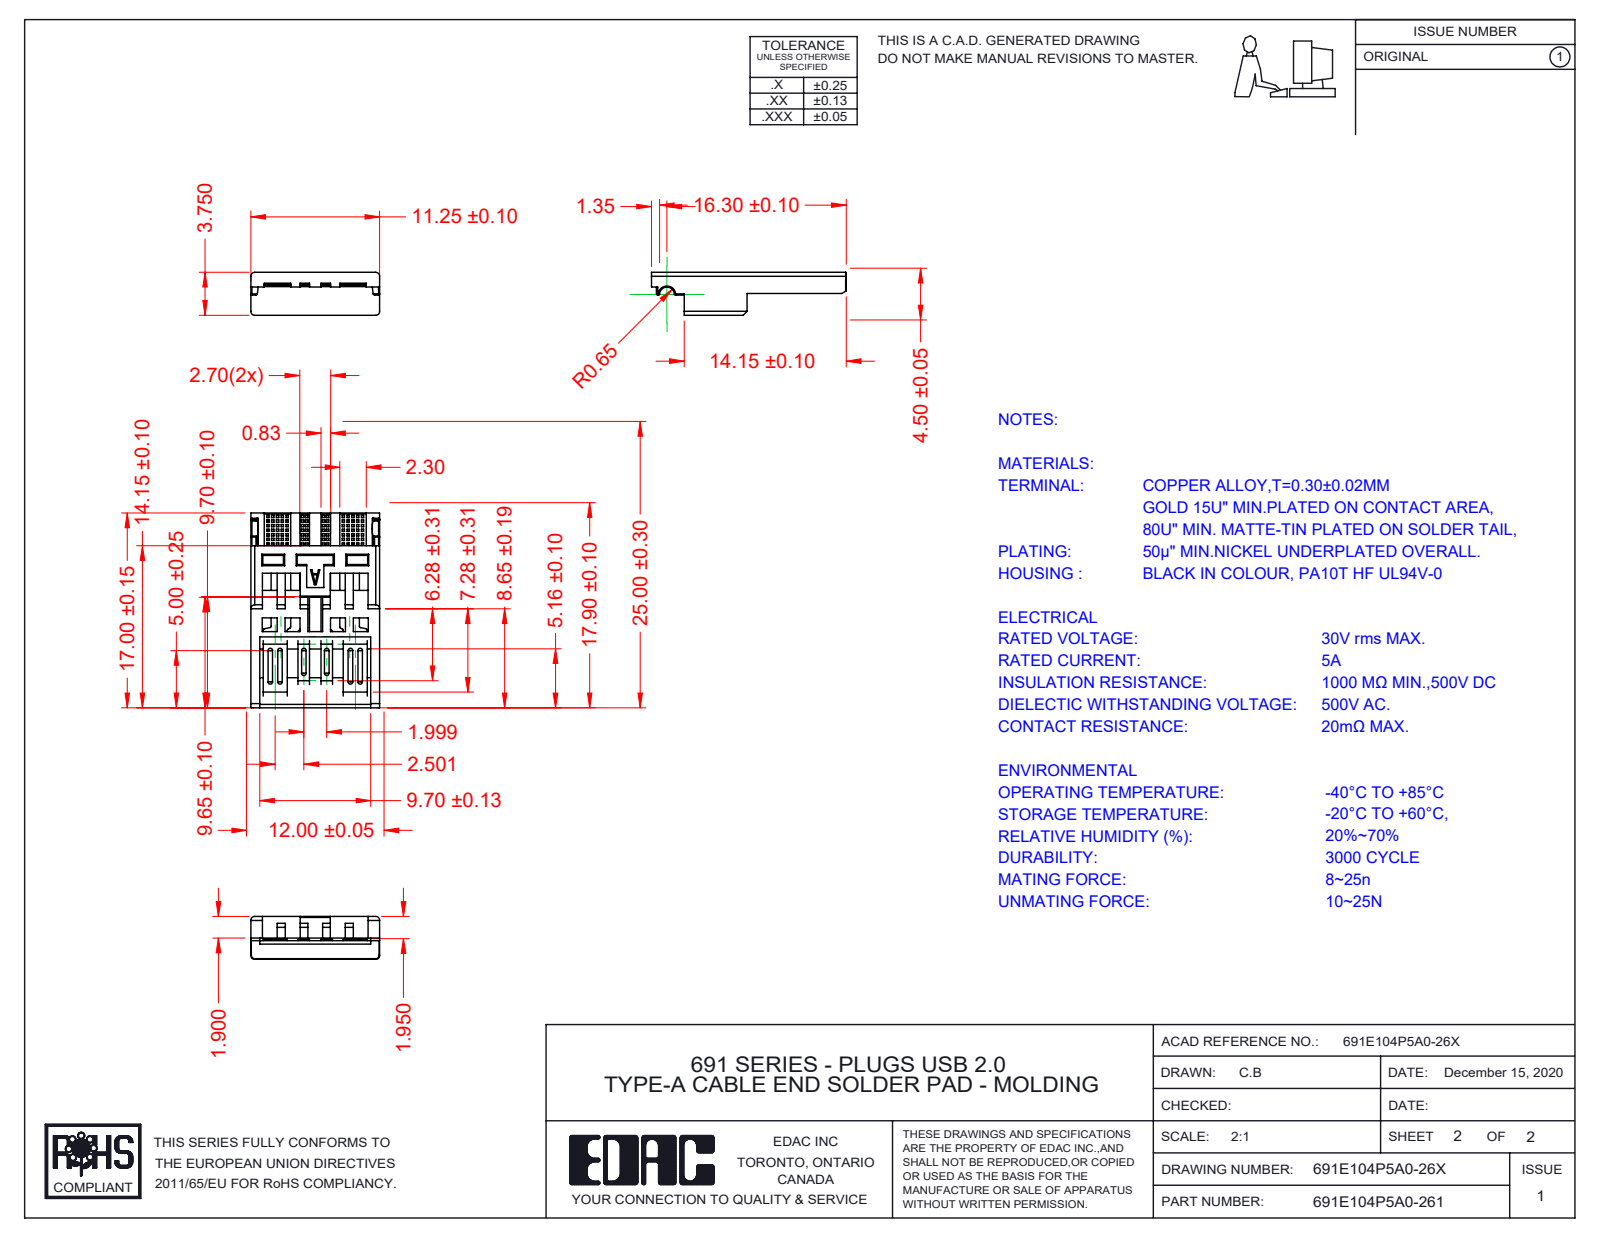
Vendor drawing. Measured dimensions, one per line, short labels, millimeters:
name: PIN1 691E104P5A0-26X; HOUSING 691E104P5A0-26X_Black; SHELL 691E104P5A0-26X_Open; PIN2 691E104P5A0-26X (+3 more)
written by: SolidWorks 2020 (AUTOMOTIVE_DESIGN)
unit: mm
bodies: 6 solids, 1302 faces (991 planar, 237 cylindrical, 74 other)
size: 26.08 × 12.46 × 12
volume: 568 mm³; area: 2 324 mm²
rounds: 27× R0.1, 20× R0.45, 16× R0.13, 14× R0.3, 13× R0.15, 13× R0.5, 12× R0.19, 12× R0.21
face distances: 0.35, 4.15, 4.5, 3.8, 11.65, 1, 1.3, 0.49, 1.85, 1.6
